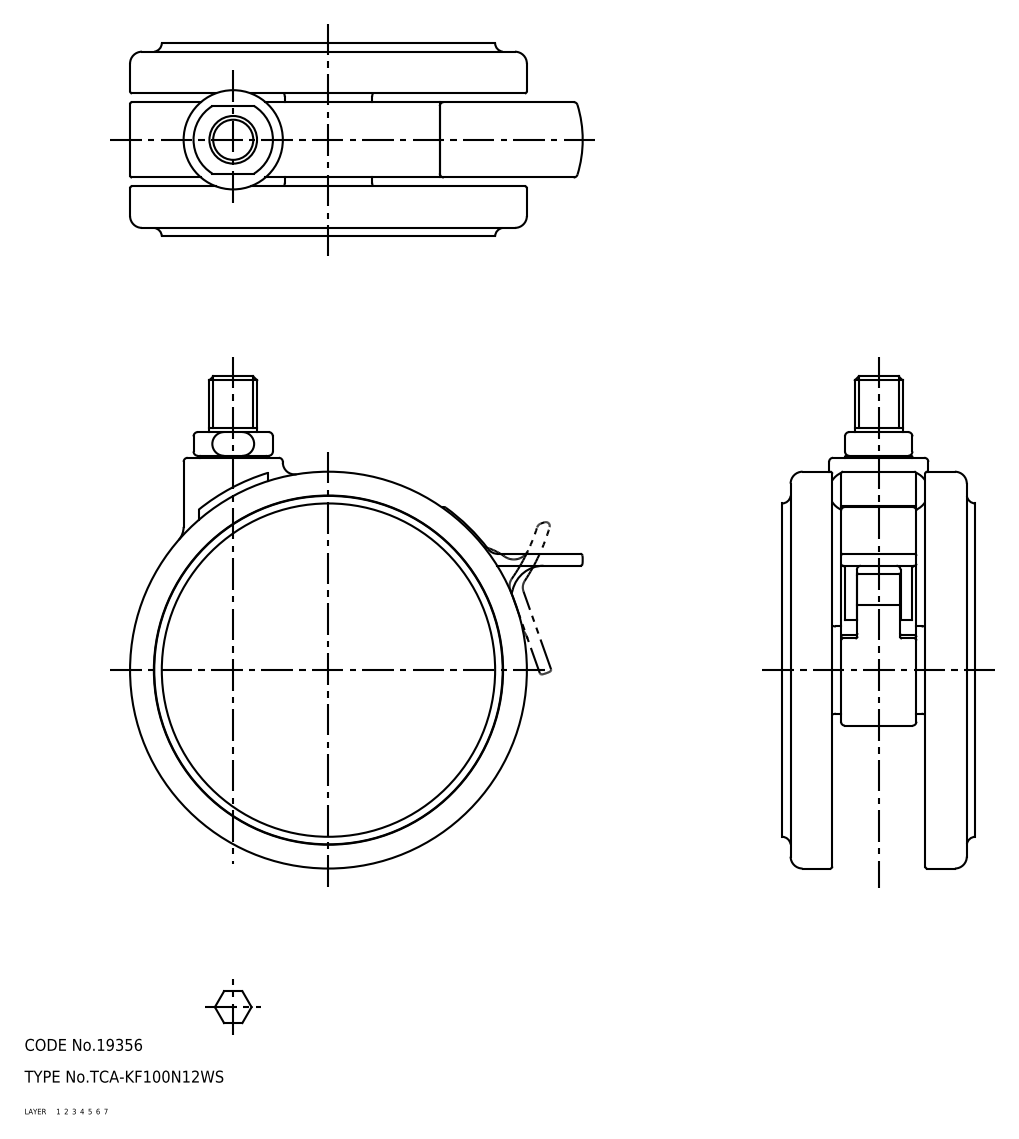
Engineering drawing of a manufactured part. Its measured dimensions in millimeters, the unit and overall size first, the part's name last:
Units: millimetres
Overall size (bounding box): 124 × 114.07 × 48.6
Round holes (diameter × count): ⌀2.4 ×1, ⌀3 ×1, ⌀3.3 ×1, ⌀3.6 ×1, ⌀5.8 ×1, ⌀6.1 ×1, ⌀8.07 ×1, ⌀9 ×1, ⌀9.3 ×1, ⌀10.7 ×1, ⌀12.3 ×1, ⌀13 ×1
Round bosses / shafts (diameter × count): ⌀100 ×1, ⌀87.8 ×1, ⌀25 ×1, ⌀22 ×1, ⌀20 ×1, ⌀17 ×1, ⌀12 ×1, ⌀10.5 ×1
Partial cylindrical surfaces — rounded edges, fillets, slot ends (radius × count): R0.5 ×63, R1 ×61, R1.5 ×21, R0.2 ×18, R0.3 ×17, R2 ×16, R3 ×7, R0.7 ×2
Main face-to-face distances: 1.8, 45, 46.8, 3.6, 43.2, 12.6, 32.4, 9, 36, 10.8
Hole centre spacings: 21.4, 29.97, 43.99
Volume: 185 560 mm³ · Surface area: 95 672 mm²
Bodies: 1 solid, 1520 faces (528 planar, 654 cylindrical, 338 other)
Part name (STEP PRODUCT): caster; TCA_KF100N12WS
STEP written by: SolidWorks 2015 (AUTOMOTIVE_DESIGN)
